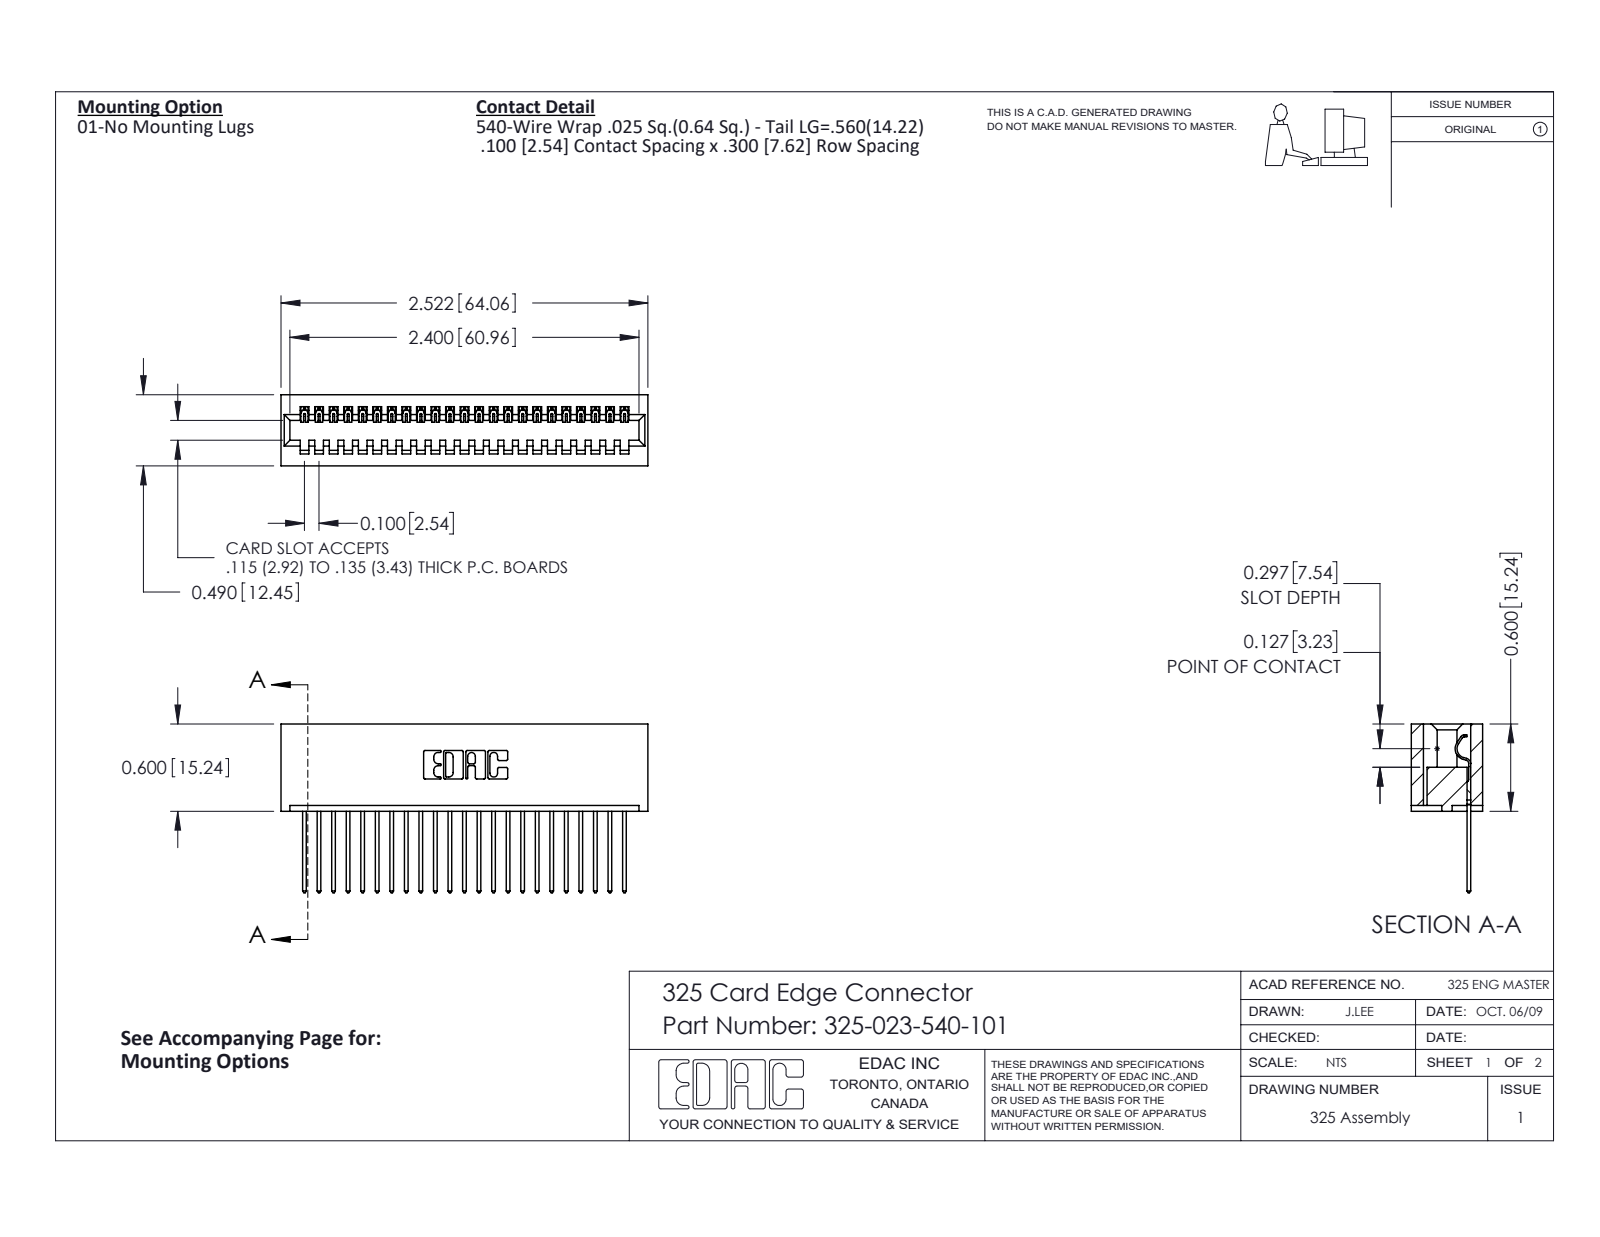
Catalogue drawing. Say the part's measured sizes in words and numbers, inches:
The part is named "325-292-001_325-293-140; 325-023-540-101; 325 Part_Lugless". Its 3-D file was written by "SolidWorks 2016 (CONFIG_CONTROL_DESIGN)". It is 24 solids with 1440 faces: 1032 planar, 408 cylindrical and 0 other. Overall it measures 2.522 by 1.16 by 0.49 inches. Its volume is 0.524 cubic inches and its surface area 15.16 square inches. Partial cylindrical surfaces (rounded edges, fillets, slot ends): 46 of radius 0.006, 46 of radius 0.01, 22 of radius 0.01, 6 of radius 0.007, 6 of radius 0.031, 3 of radius 0.026, 1 of radius 0.014, 1 of radius 0.022. The main face-to-face distances are 0.083, 0.407, 0.3, 0.49, 0.107, 0.383, 0.025, 0.56, 0.325, 0.1.
